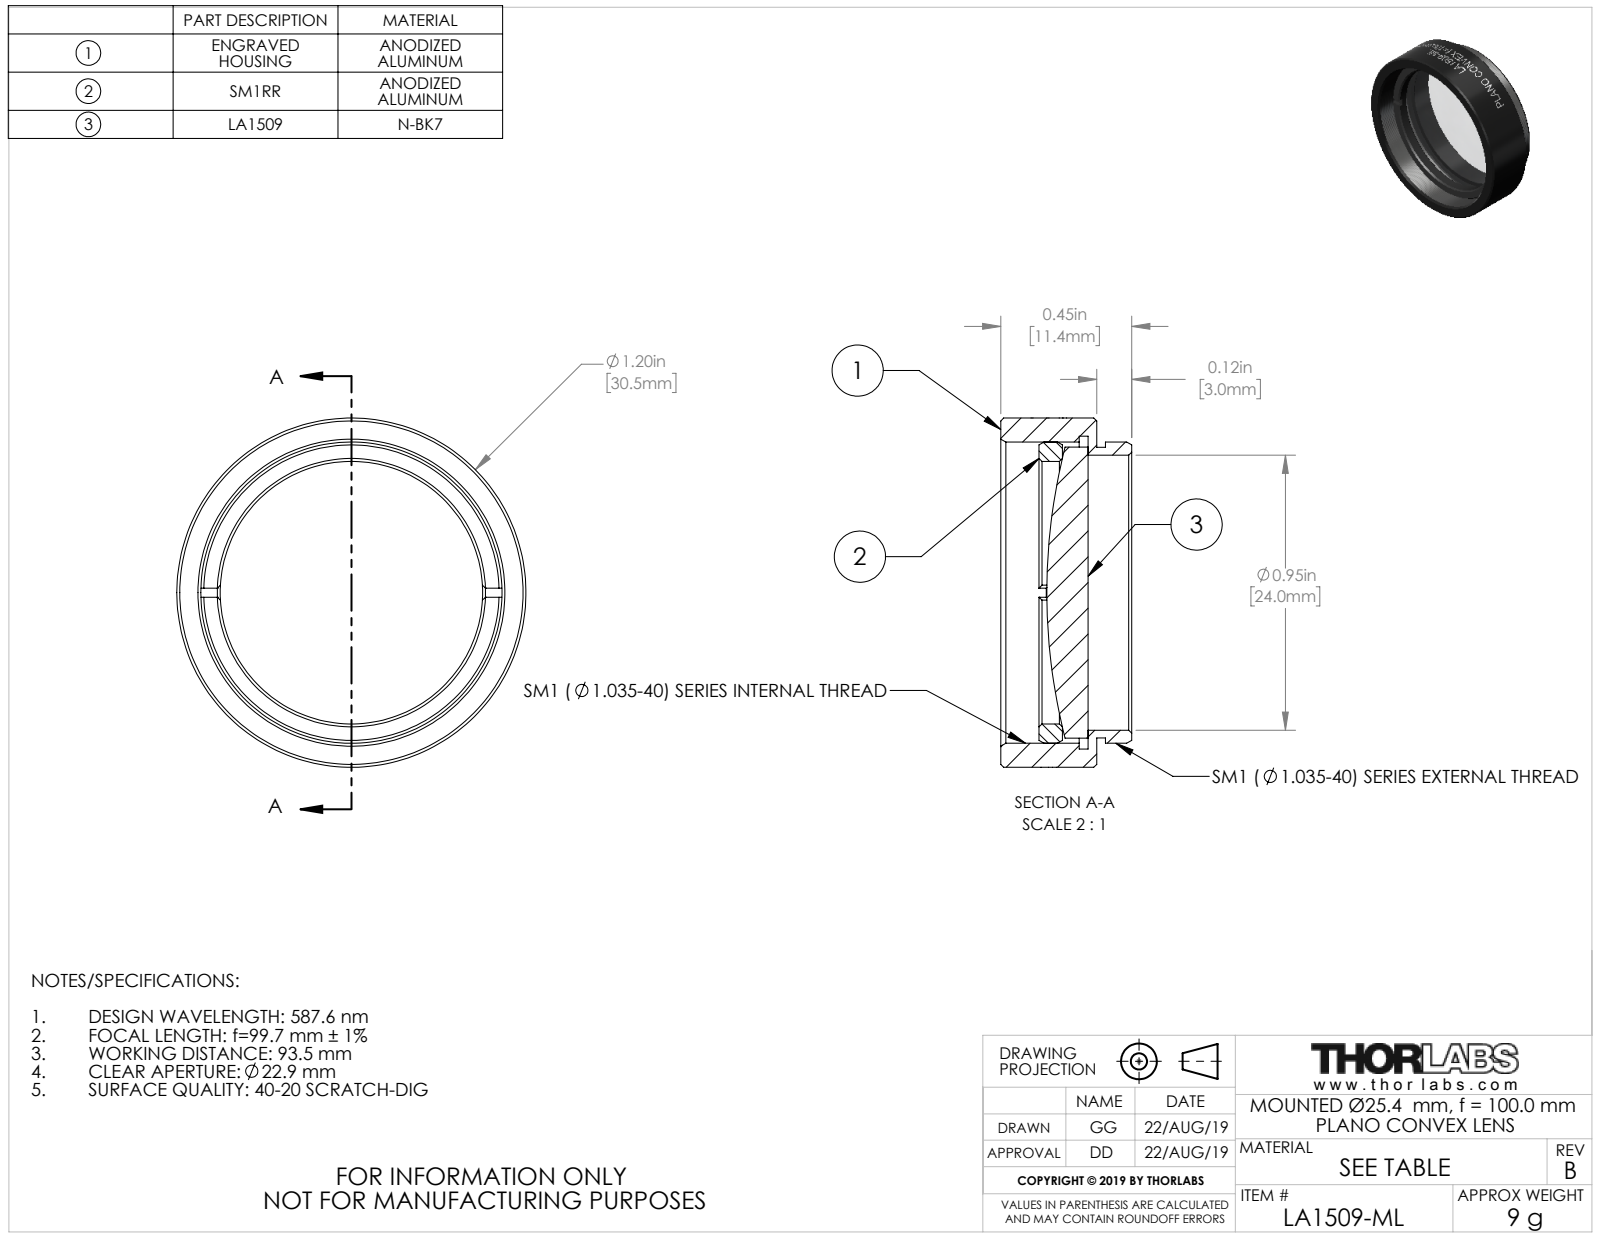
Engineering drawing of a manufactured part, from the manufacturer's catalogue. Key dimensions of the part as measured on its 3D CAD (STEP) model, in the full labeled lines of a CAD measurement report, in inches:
Part name (STEP PRODUCT): 24410-E0W
STEP written by: SolidWorks 2018 (CONFIG_CONTROL_DESIGN)
Units: inches
Bodies: 3 solids, 119 faces (20 planar, 75 cylindrical, 24 other)
Overall size (bounding box): 1.2 × 1.2 × 0.45
Volume: 0.214 in³ · Surface area: 6.696 in²
Round holes (diameter × count): ⌀0.902 ×1, ⌀0.945 ×1, ⌀1.075 ×1
Round bosses / shafts (diameter × count): ⌀1.2 ×1, ⌀1.035 ×1, ⌀1 ×1, ⌀0.999 ×1
Main face-to-face distances: 0.03, 0.33, 0.3, 0.118, 0.088, 0.212, 0.198, 0.168, 0.08, 0.132
